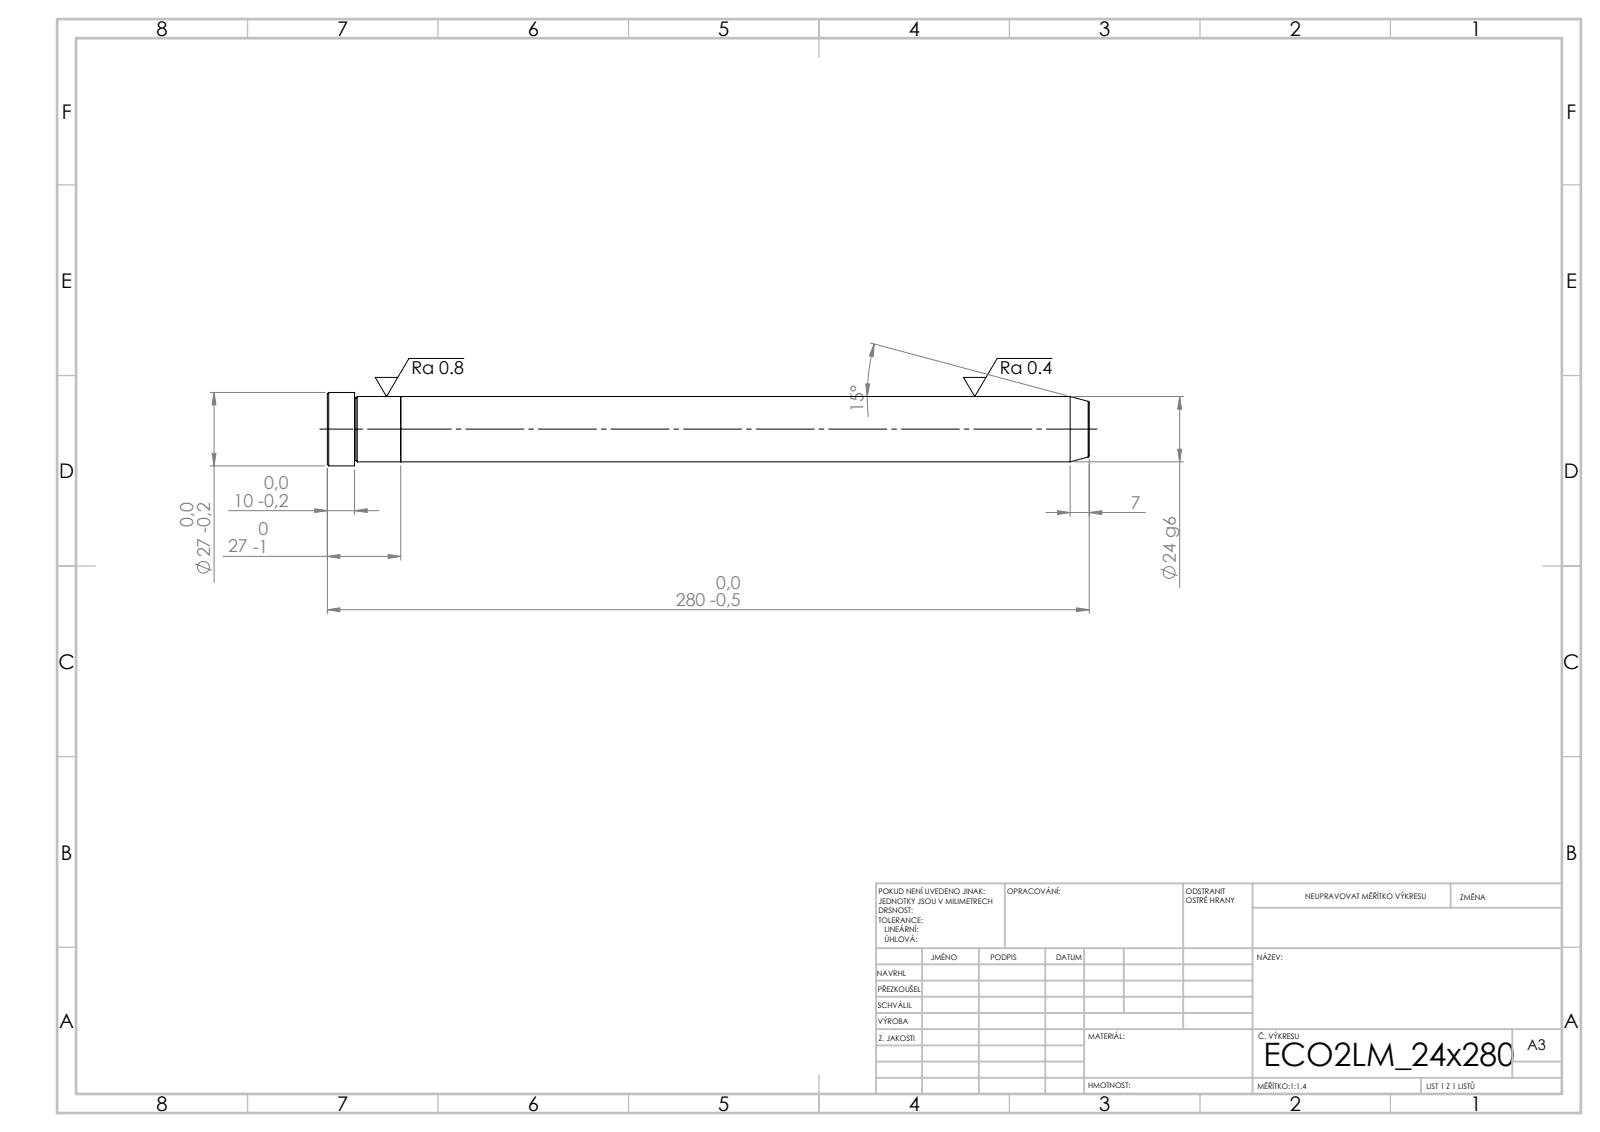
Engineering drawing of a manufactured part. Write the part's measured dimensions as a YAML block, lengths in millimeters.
step_written_by: "SolidWorks 2019 (CONFIG_CONTROL_DESIGN)"
units: millimeters
bodies: {solids: 2, faces: 21, planar: 5, cylindrical: 6, other: 10}
overall_size: [280, 27, 27]
volume: 127360
surface_area: 23109
round_bosses_or_shafts:
  - {diameter: 27, count: 1}
  - {diameter: 24, count: 1}
face_to_face_distances: [27, 253, 280, 270, 17, 10]
